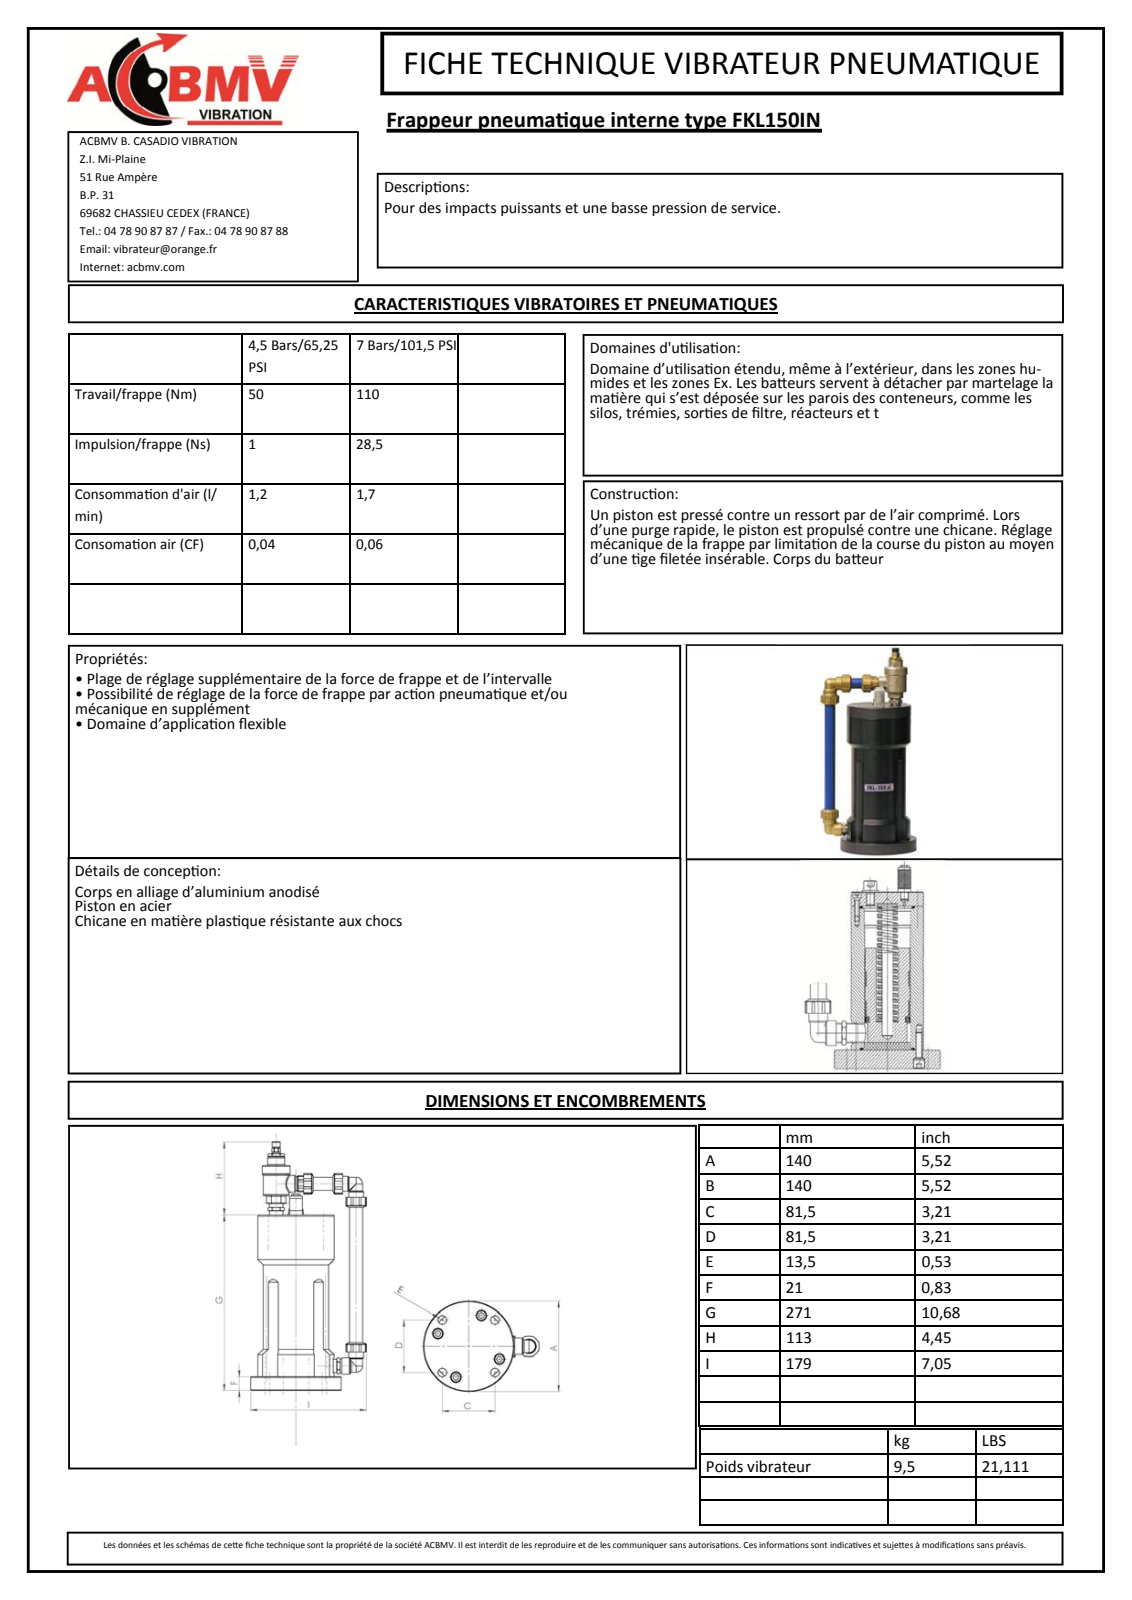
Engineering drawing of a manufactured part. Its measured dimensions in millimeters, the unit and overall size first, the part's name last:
Units: millimetres
Overall size (bounding box): 384 × 179 × 140
Round holes (diameter × count): ⌀13.5 ×10, ⌀6.65 ×6, ⌀8.5 ×6, ⌀8.38 ×4, ⌀10.5 ×4, ⌀10.7 ×4, ⌀16.5 ×4, ⌀16 ×3, ⌀14 ×2, ⌀18 ×2, ⌀19.48 ×2, ⌀6 ×1
Round bosses / shafts (diameter × count): ⌀13 ×6, ⌀8 ×6, ⌀10 ×5, ⌀16 ×4, ⌀26 ×3, ⌀23 ×2, ⌀20.95 ×2, ⌀20 ×2
Partial cylindrical surfaces — rounded edges, fillets, slot ends (radius × count): R1 ×6, R1.5 ×6, R18.5 ×4, R16 ×2, R16.5 ×2, R6.6 ×1, R10 ×1, R12.5 ×1
Main face-to-face distances: 271, 21, 250, 20, 2.05, 227.95, 2, 10, 30, 22
Hole centre spacings: 49.25, 22.06, 41.56, 42.44, 42.83, 51.5, 57.5, 60.77
Volume: 2 700 000 mm³ · Surface area: 239 742 mm²
Bodies: 3 solids, 986 faces (365 planar, 251 cylindrical, 370 other)
Part name (STEP PRODUCT): 4150-00-M
STEP written by: Autodesk Inventor 2011 (CONFIG_CONTROL_DESIGN)
